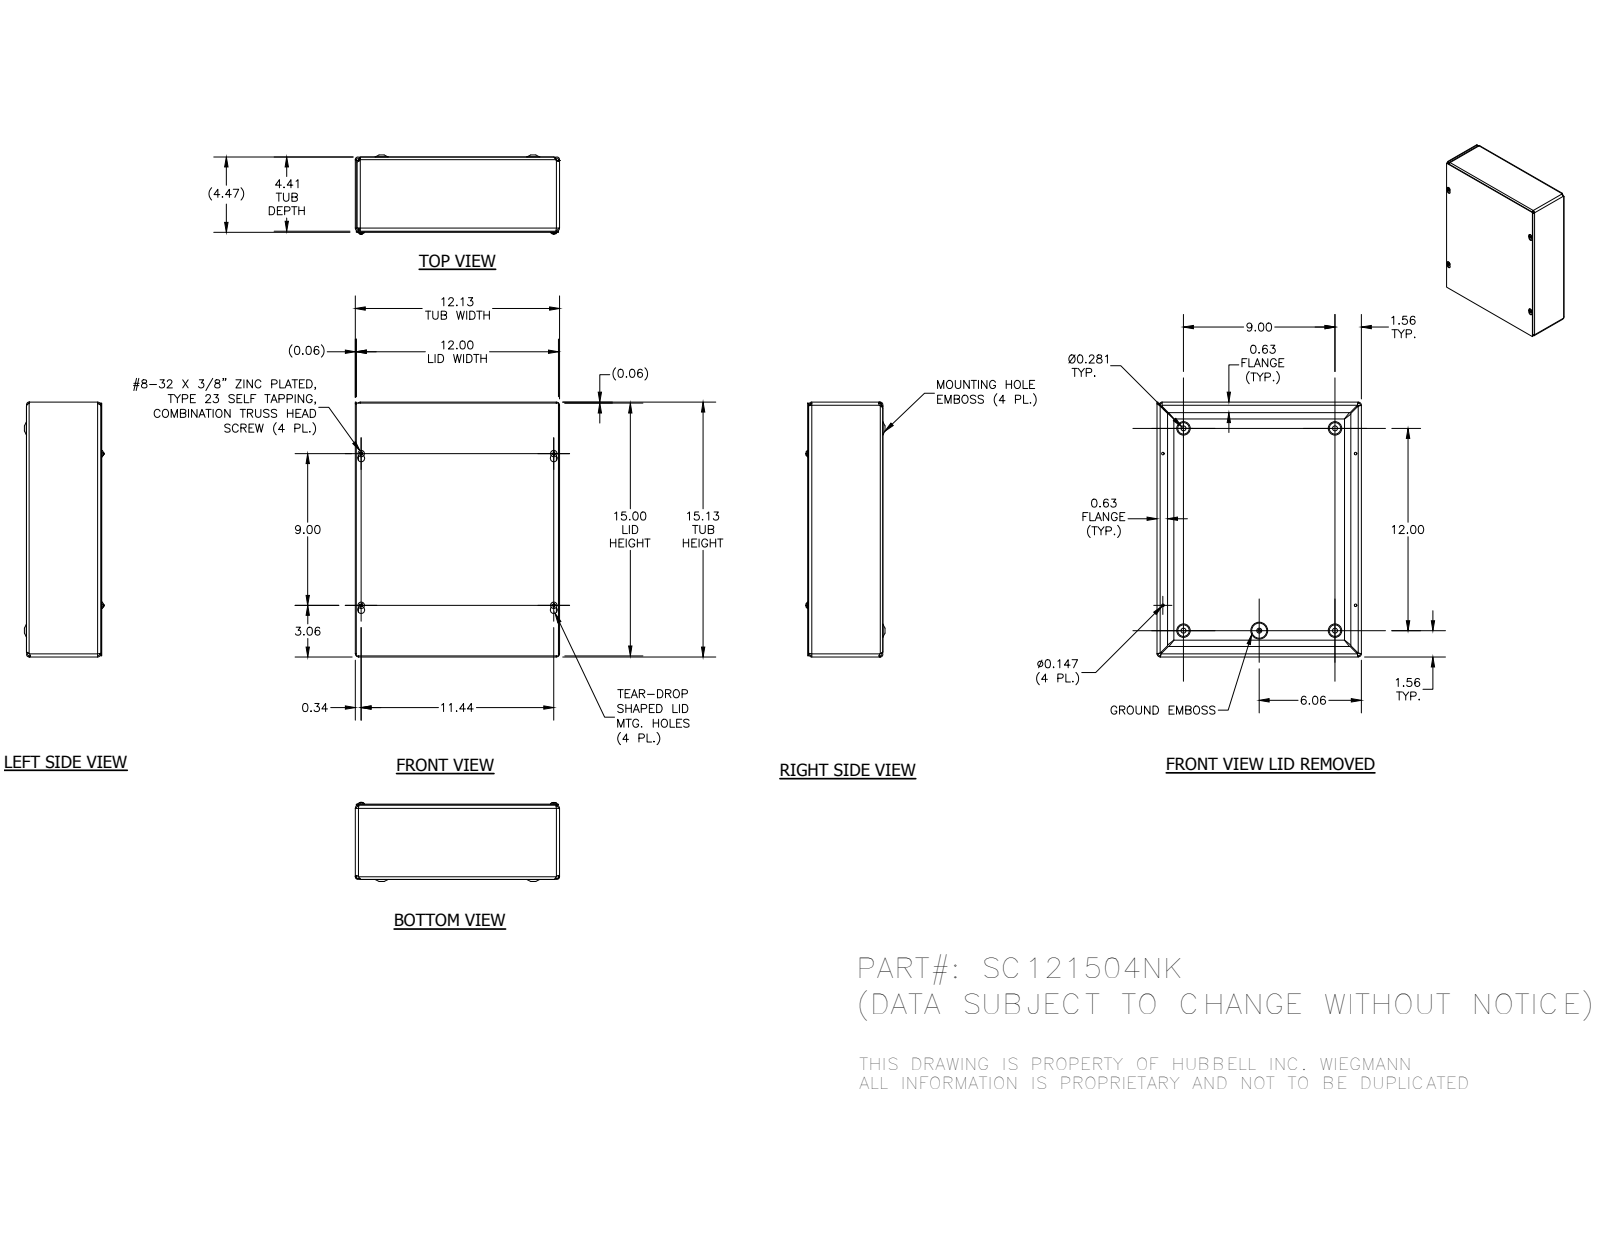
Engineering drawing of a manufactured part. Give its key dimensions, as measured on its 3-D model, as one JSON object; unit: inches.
{"part_name": "SC1215BKP; SC121504NKWRA; SC1215LID; 34056 (+1 more)", "step_written_by": "Autodesk Inventor 2014 (AUTOMOTIVE_DESIGN)", "units": "inches", "bodies": {"solids": 7, "faces": 357, "planar": 132, "cylindrical": 67, "other": 158}, "overall_size": [15.125, 12.125, 4.693], "volume_in3": 41.02, "surface_area_in2": 1336, "round_holes": [[0.147, 4], [0.3, 4], [0.165, 1]], "round_bosses_or_shafts": [[0.384, 4], [0.164, 4], [0.228, 1]], "partial_cylinders_radius": [[0.125, 12], [0.187, 8], [0.055, 4], [0.062, 4], [0.094, 4], [0.117, 4], [0.124, 4], [0.156, 4]], "face_to_face_distances": [0.062, 4.343, 4.405, 0.063, 4.406, 4.468, 15.063, 0.062, 12.063, 12.001], "hole_center_spacings": [1.933, 9, 10.57, 4.5, 10.328, 10.328, 11.437, 11.956]}
